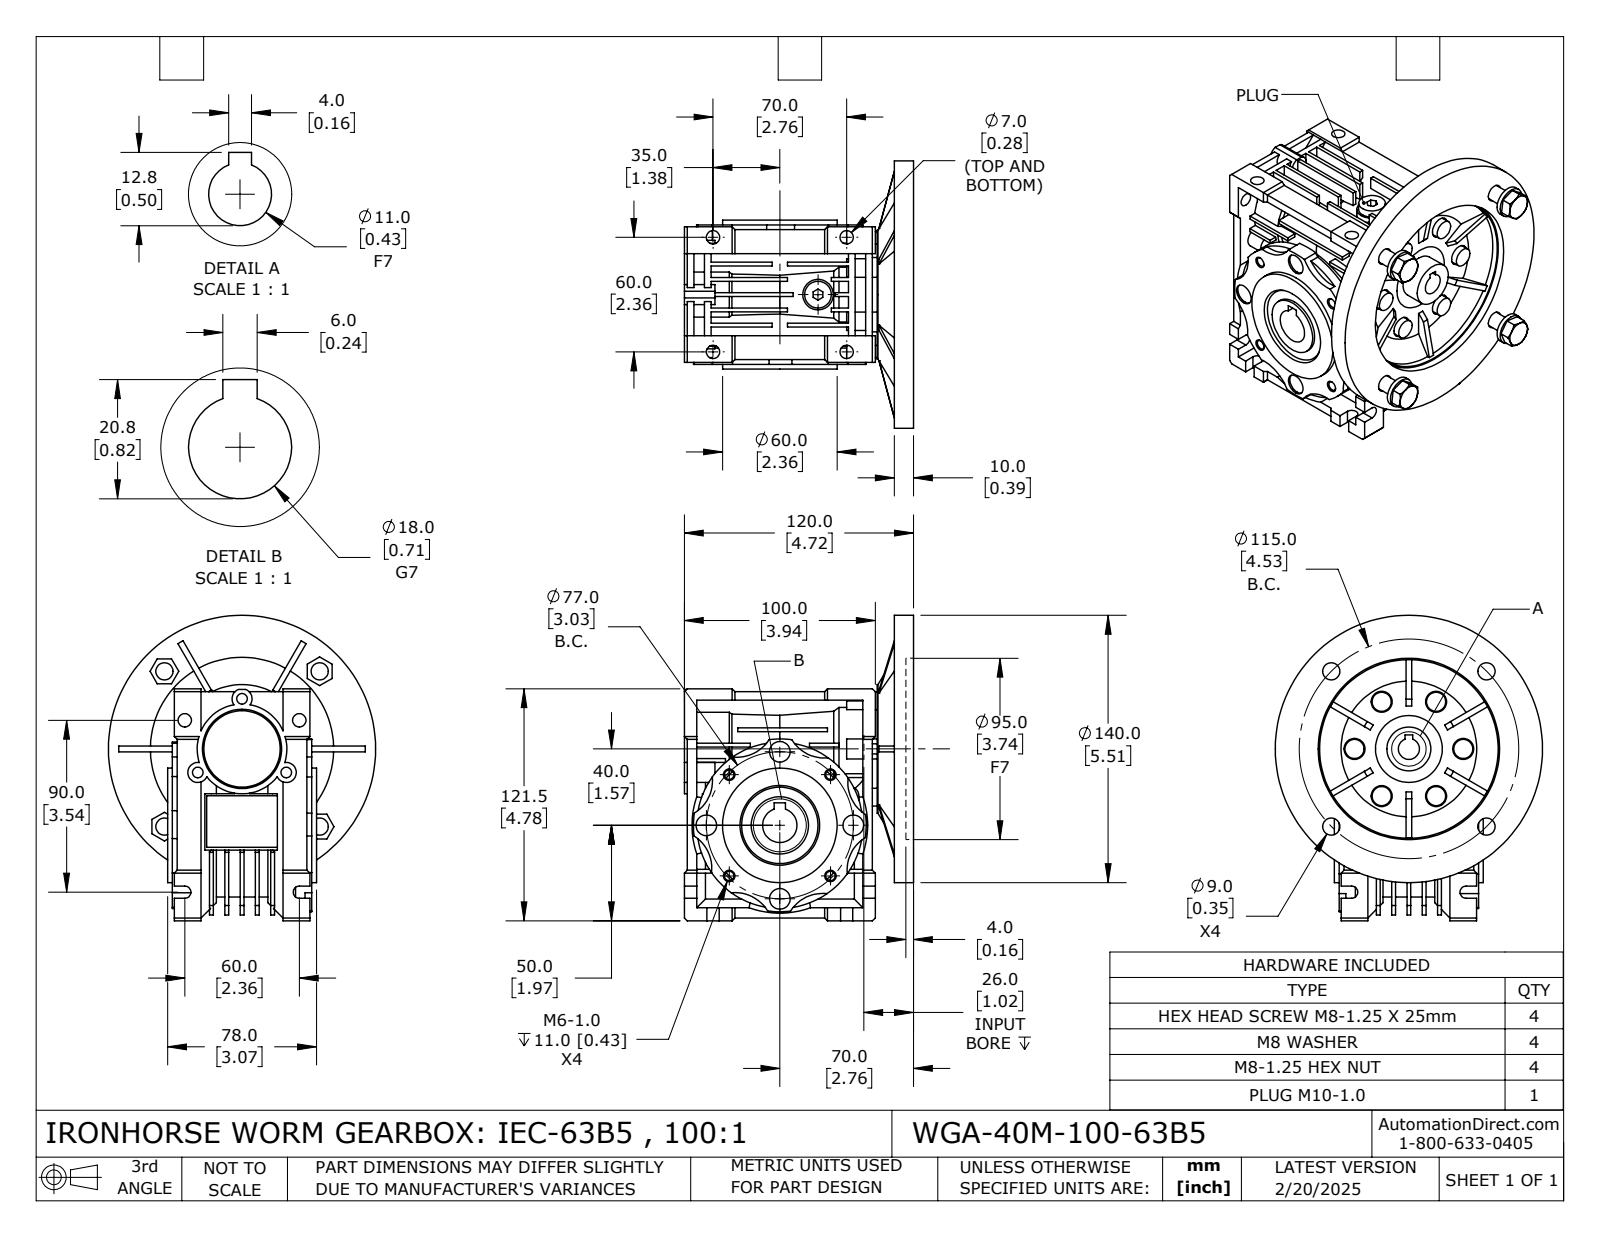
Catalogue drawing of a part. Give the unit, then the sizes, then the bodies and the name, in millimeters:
Units: millimetres
Overall size (bounding box): 160 × 140 × 137.98
Round holes (diameter × count): ⌀11 ×7, ⌀7 ×6, ⌀9 ×5, ⌀4.92 ×4, ⌀6.8 ×4, ⌀8 ×4, ⌀9.12 ×4, ⌀10.8 ×4, ⌀5.55 ×3, ⌀11.5 ×1, ⌀18 ×1, ⌀23 ×1
Round bosses / shafts (diameter × count): ⌀10 ×6, ⌀16 ×5, ⌀140 ×1, ⌀75 ×1, ⌀67.5 ×1, ⌀60 ×1, ⌀54 ×1, ⌀47 ×1
Partial cylindrical surfaces — rounded edges, fillets, slot ends (radius × count): R20 ×8, R3.2 ×6, R5.22 ×6, R5.25 ×3, R43.5 ×1, R43.59 ×1, R45.25 ×1, R46 ×1
Main face-to-face distances: 10, 8, 6, 2, 5, 1.5, 16, 24, 14, 2.5
Hole centre spacings: 28.5, 29.1, 70.22, 49.36, 30.87, 33.54, 37.5, 38.5
Volume: 749 957 mm³ · Surface area: 190 617 mm²
Bodies: 18 solids, 1083 faces (592 planar, 298 cylindrical, 193 other)
Part name (STEP PRODUCT): WGA-40M-100-63B5
STEP written by: SolidWorks 2024 (CONFIG_CONTROL_DESIGN)
